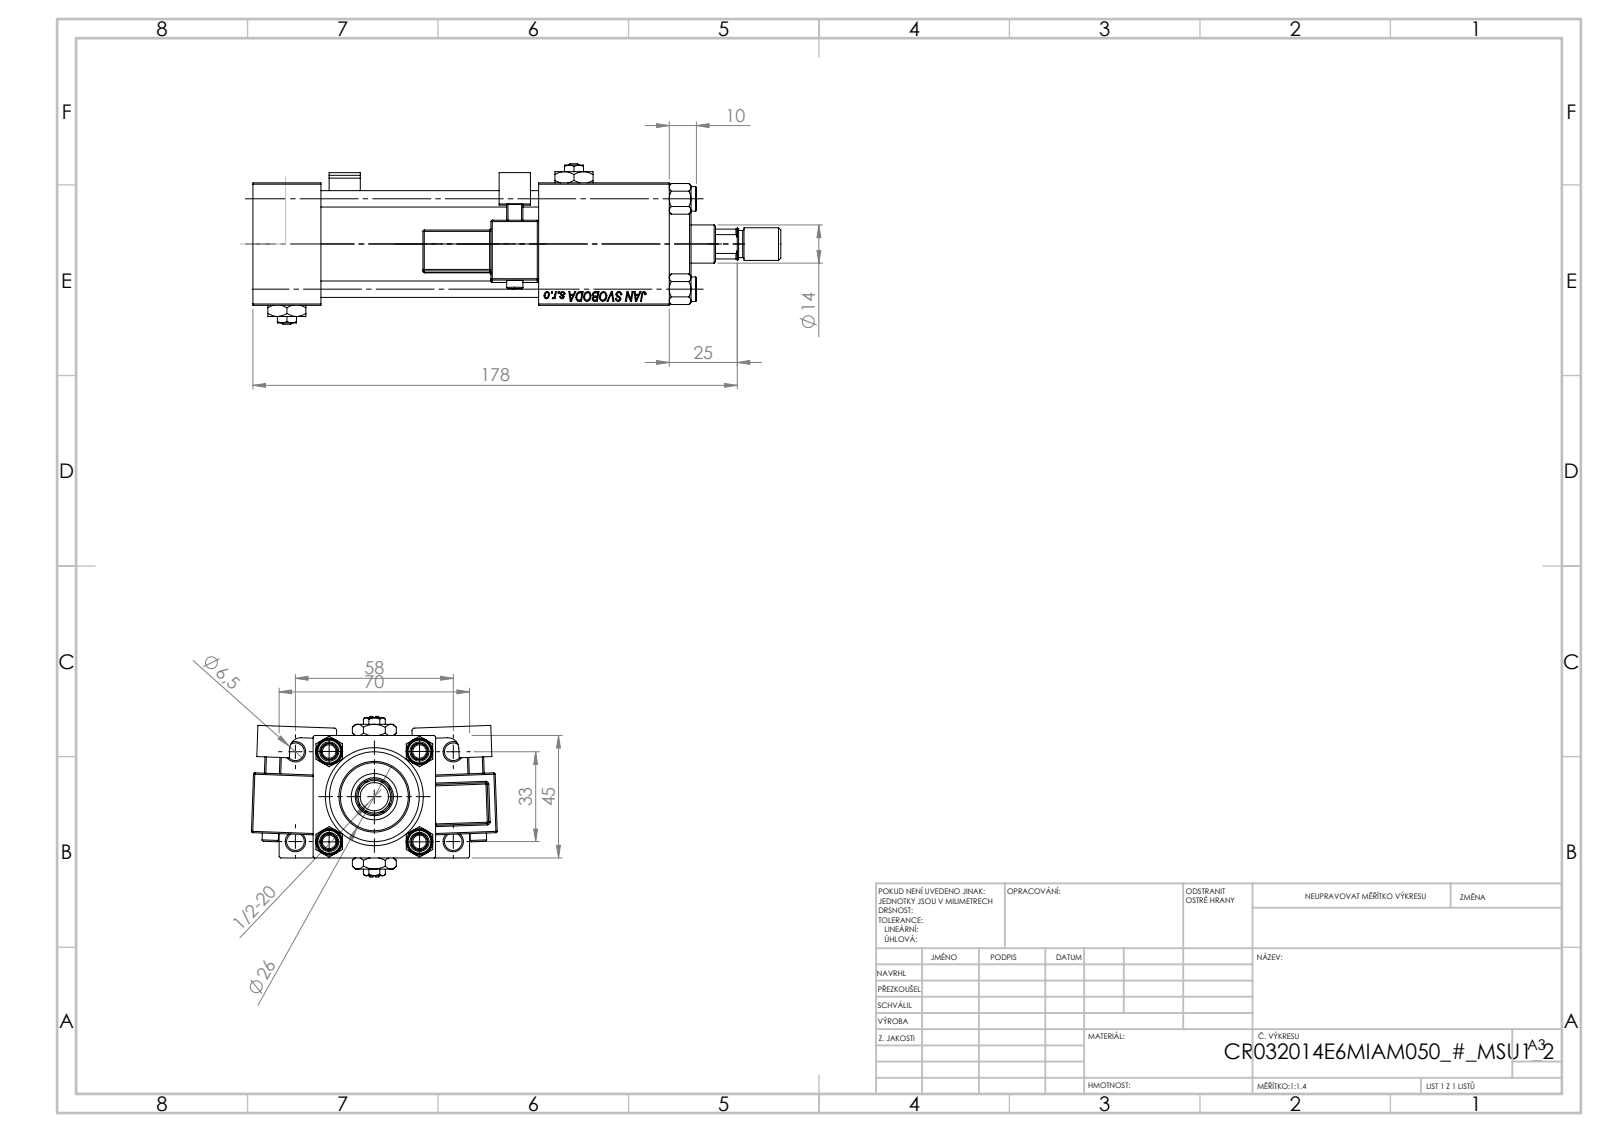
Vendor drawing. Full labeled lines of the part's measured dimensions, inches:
Part name (STEP PRODUCT): V215CR_MSU; ROD_END_AH; V215CR_E_Body; V215CR_TYCINKA_E (+4 more)
STEP written by: SolidWorks 2019 (CONFIG_CONTROL_DESIGN)
Units: inches
Bodies: 16 solids, 1401 faces (608 planar, 157 cylindrical, 636 other)
Overall size (bounding box): 7.638 × 3.556 × 2.323
Volume: 17.08 in³ · Surface area: 156.6 in²
Round holes (diameter × count): ⌀0.256 ×5, ⌀0.236 ×4, ⌀0.276 ×3, ⌀0.518 ×3, ⌀0.787 ×3, ⌀0.551 ×1, ⌀0.669 ×1, ⌀0.945 ×1, ⌀1.26 ×1, ⌀1.299 ×1
Round bosses / shafts (diameter × count): ⌀0.354 ×4, ⌀0.236 ×2, ⌀1.496 ×1, ⌀1.024 ×1, ⌀0.472 ×1, ⌀0.394 ×1
Partial cylindrical surfaces — rounded edges, fillets, slot ends (radius × count): R0.02 ×48, R0.039 ×2, R0.098 ×2, R0.157 ×2, R0.256 ×1
Main face-to-face distances: 1.772, 0.984, 0.492, 0.118, 2.264, 1.89, 4.134, 3.15, 6.024, 0.905
Hole centre spacings: 0.488, 0.924, 1.307, 1.314, 1.392, 1.795, 2.219, 1.299
